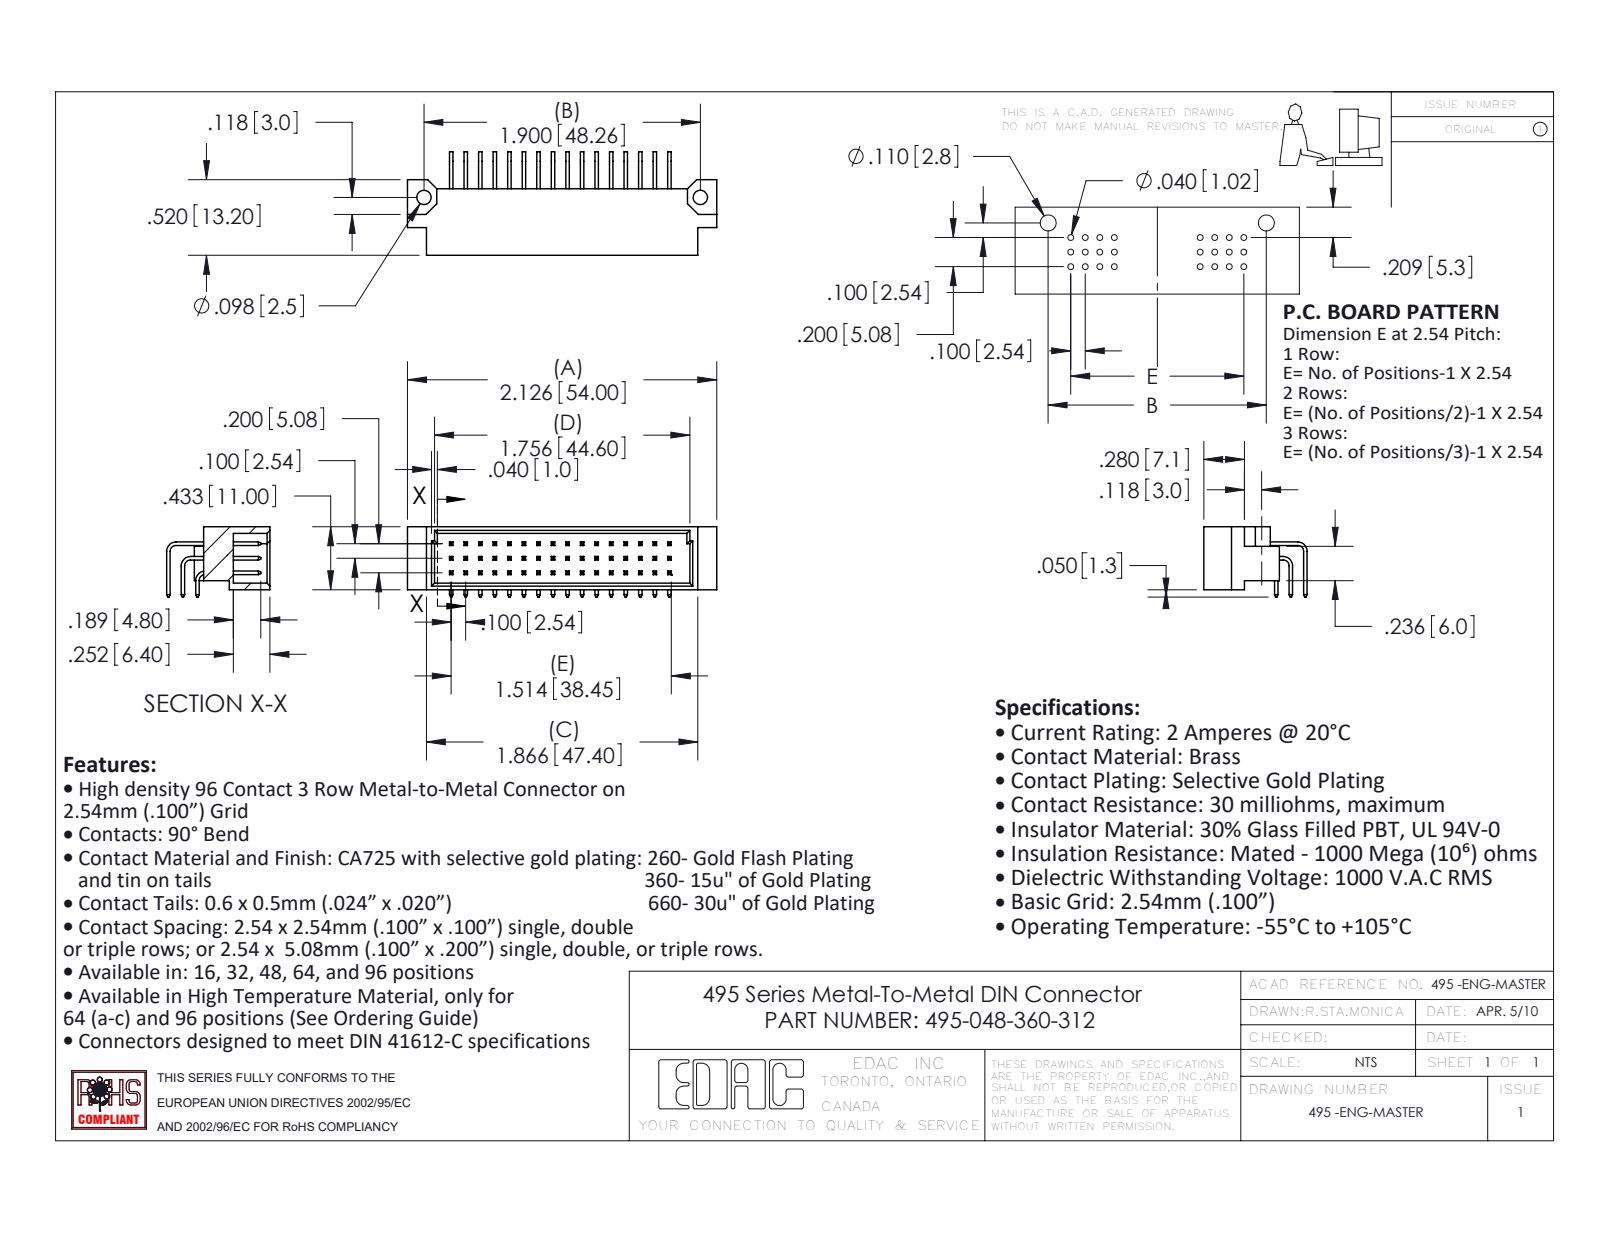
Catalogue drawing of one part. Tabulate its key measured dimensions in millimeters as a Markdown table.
| quantity | value |
| --- | --- |
| part name | 495-048-360-312; 495-290-2; 495 Part_48; 495-290-1 (+1 more) |
| STEP written by | SolidWorks 2020 (AUTOMOTIVE_DESIGN) |
| units | millimeters |
| bodies | 49 solids, 1106 faces (1006 planar, 100 cylindrical, 0 other) |
| overall size | 54 × 18.05 × 12.27 |
| volume | 3 795 mm³ |
| surface area | 6 262 mm² |
| round holes (diameter × count) | 2.49 × 2 |
| partial cylindrical surfaces (radius × count) | 1.02 × 3, 1.65 × 3 |
| main face-to-face distances | 2.54, 5.08, 0.61, 7.62, 5.2, 10.16, 1.14, 9.86, 12.7, 15.24 |
| hole center spacings | 48.26 |
